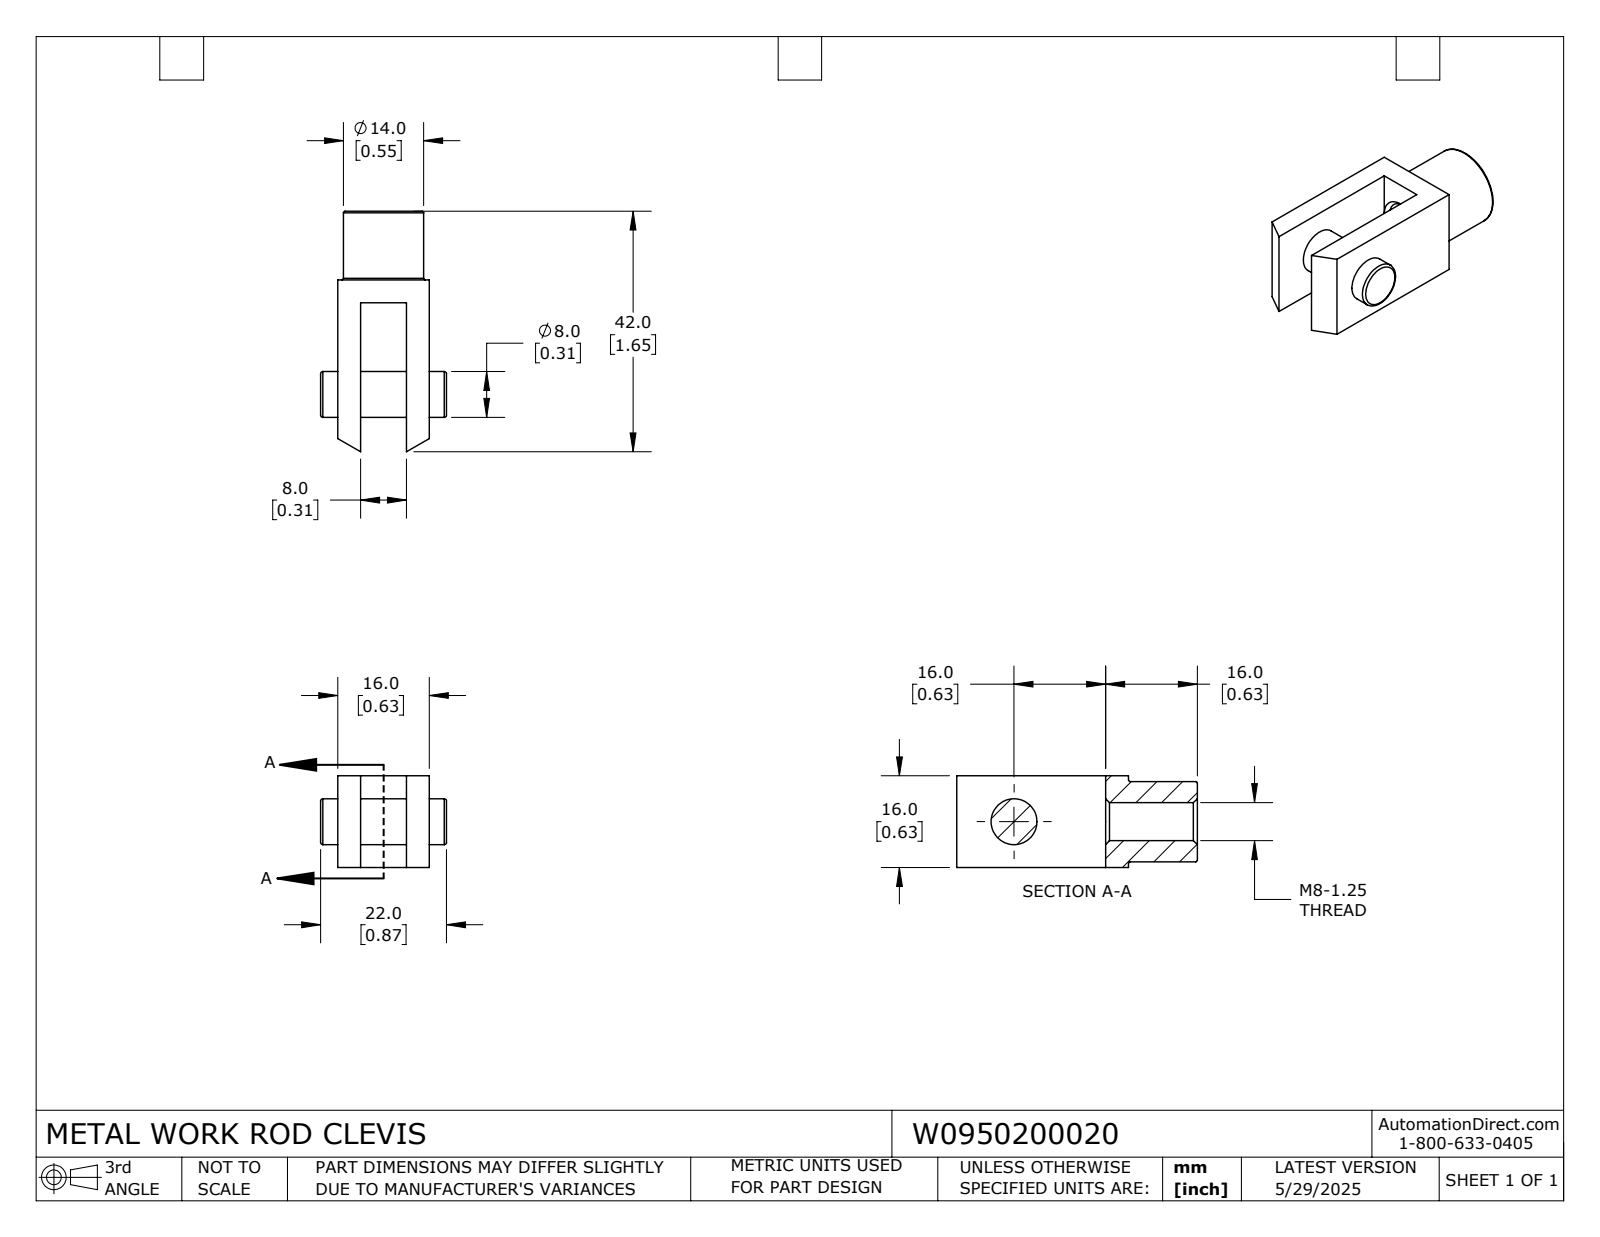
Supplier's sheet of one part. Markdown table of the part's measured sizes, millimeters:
| quantity | value |
| --- | --- |
| part name | W0950200020 |
| STEP written by | SolidWorks 2024 (CONFIG_CONTROL_DESIGN) |
| units | millimeters |
| bodies | 1 solid, 36 faces (14 planar, 10 cylindrical, 12 other) |
| overall size | 42 × 22 × 16 |
| volume | 6 188 mm³ |
| surface area | 3 785 mm² |
| round holes (diameter × count) | 6.65 × 1 |
| round bosses / shafts (diameter × count) | 14 × 1, 8 × 1 |
| main face-to-face distances | 12, 4, 16, 8, 3, 7, 15, 19, 22 |
